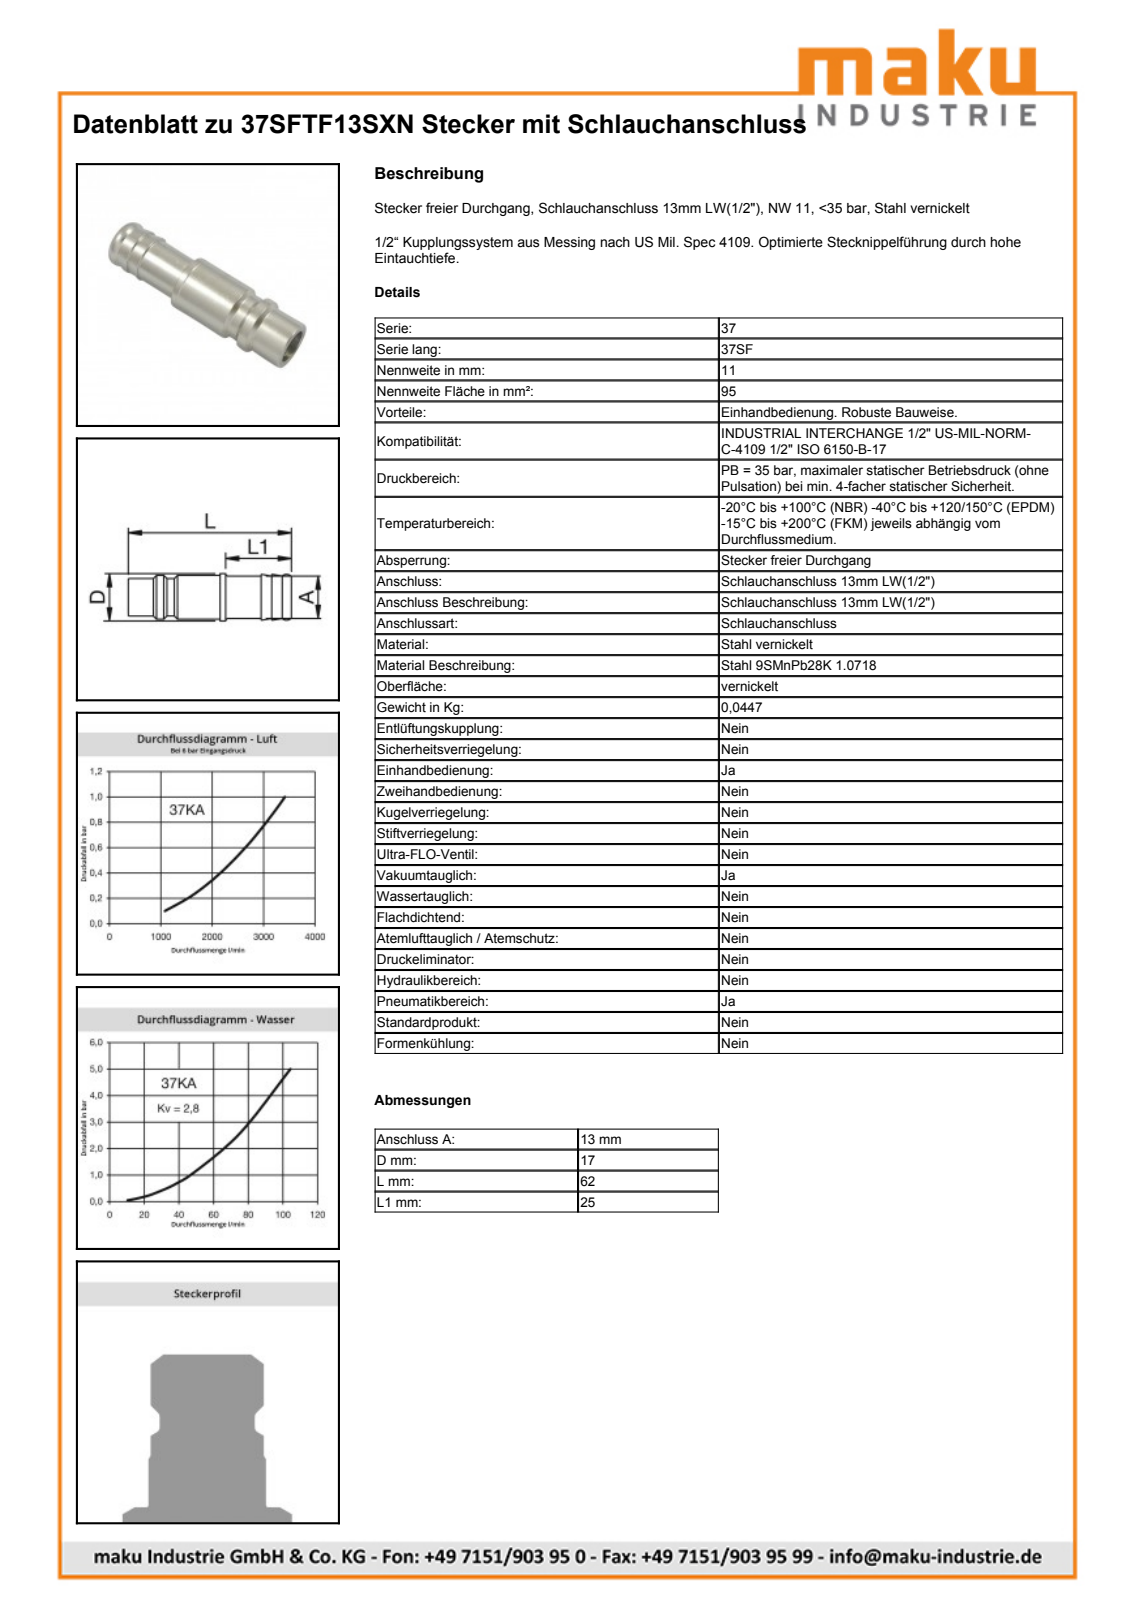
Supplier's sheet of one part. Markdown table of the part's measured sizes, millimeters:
| quantity | value |
| --- | --- |
| part name | D106865 |
| STEP written by | Autodesk Inventor 2013 (AUTOMOTIVE_DESIGN) |
| units | millimeters |
| bodies | 1 solid, 23 faces (5 planar, 7 cylindrical, 11 other) |
| overall size | 62 × 17 × 17 |
| volume | 5 940 mm³ |
| surface area | 5 171 mm² |
| round holes (diameter × count) | 10 × 1 |
| round bosses / shafts (diameter × count) | 17 × 1, 16.65 × 1, 14.25 × 1, 14.2 × 1, 13.1 × 1 |
| main face-to-face distances | 62, 37, 25, 50.5, 13.5, 11.5, 34.9, 2.1, 15.6, 27.1 |
